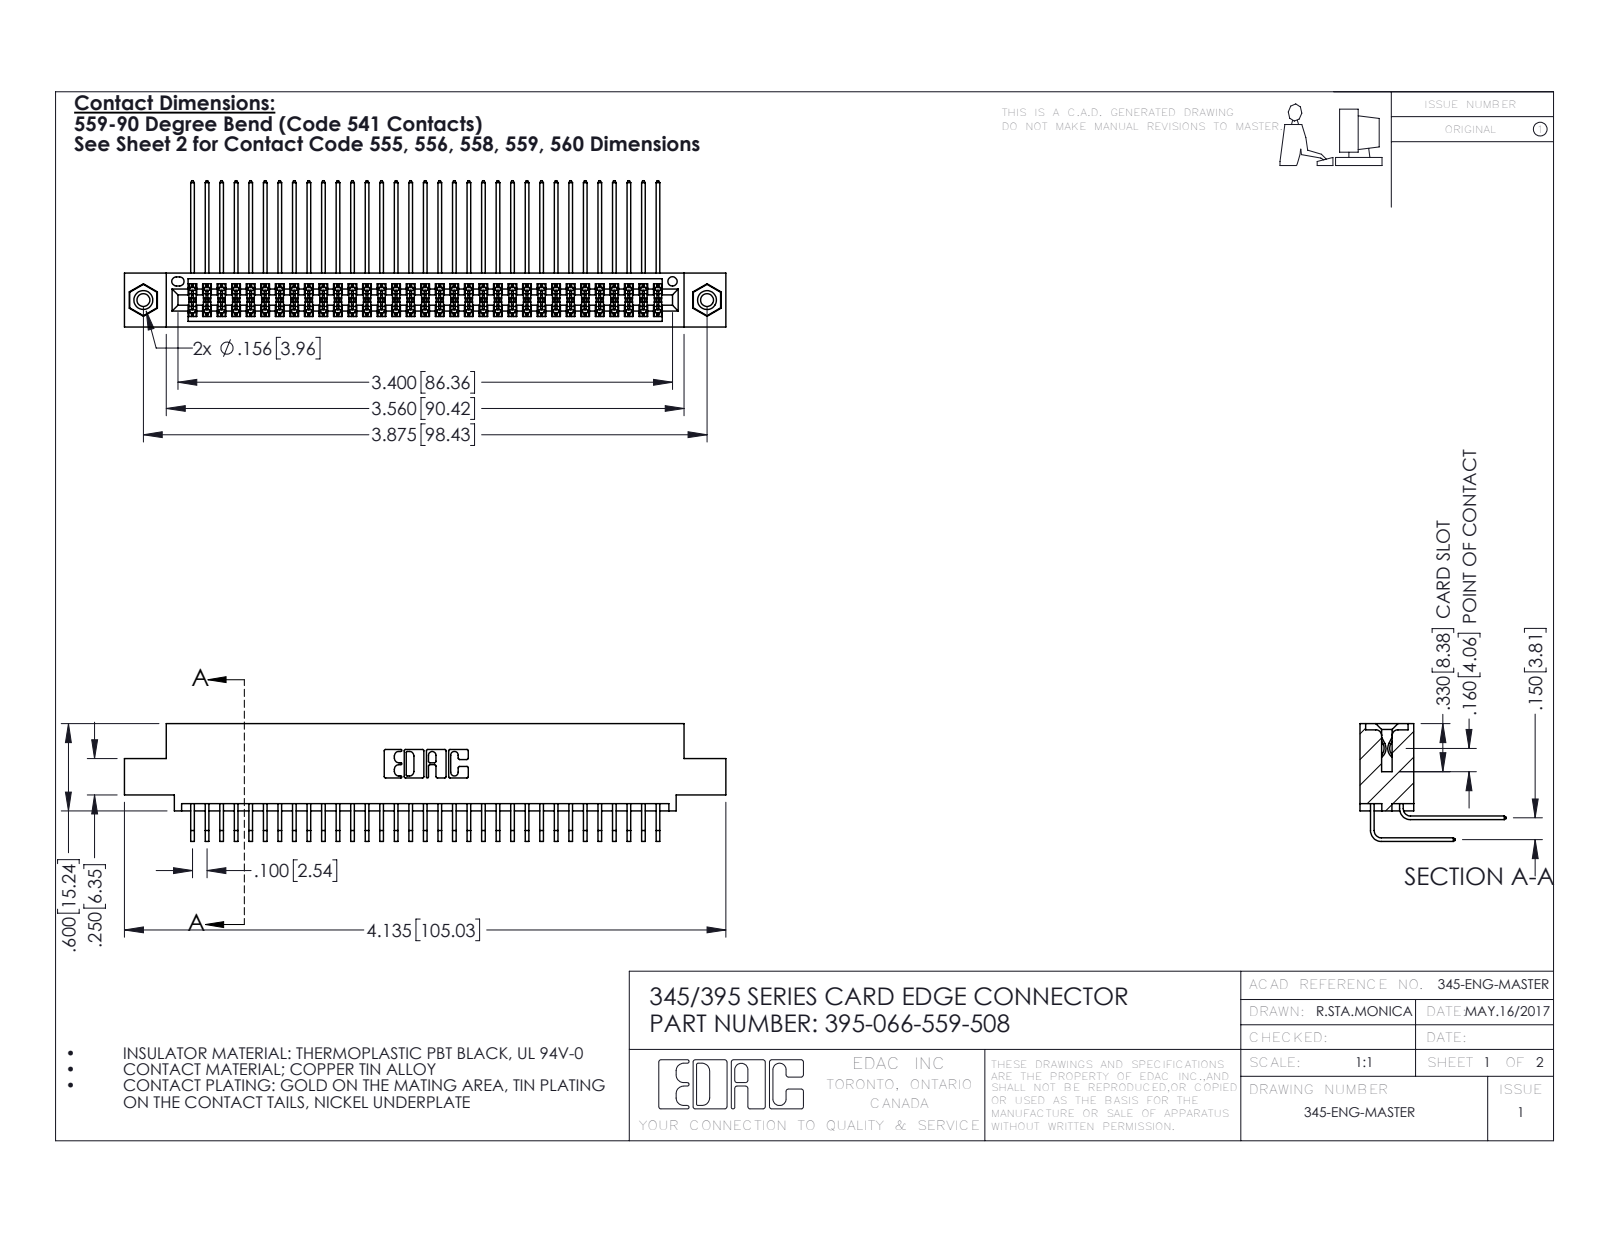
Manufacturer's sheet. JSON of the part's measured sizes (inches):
{"part_name": "345-250-001_345-250-003-102; 395-066-559-508; 345 Part_0.110 Offset - 0.156 Dia-TI; 345-292-001_558 559 Tail - 1 (+1 more)", "step_written_by": "SolidWorks 2016 (CONFIG_CONTROL_DESIGN)", "units": "inches", "bodies": {"solids": 69, "faces": 3622, "planar": 2426, "cylindrical": 1180, "other": 16}, "overall_size": [4.135, 1.005, 0.809], "volume_in3": 0.636, "surface_area_in2": 26.54, "round_holes": [[0.089, 2], [0.125, 2], [0.156, 2], [0.064, 1]], "round_bosses_or_shafts": [[0.155, 2]], "partial_cylinders_radius": [[0.006, 100], [0.01, 22], [0.007, 6], [0.031, 6], [0.026, 3], [0.014, 2], [0.019, 2], [0.022, 2]], "face_to_face_distances": [0.072, 0.298, 0.2, 0.37, 0.098, 0.272, 0.025, 0.225, 0.175, 0.15], "hole_center_spacings": [0.27, 3.64, 3.875]}
